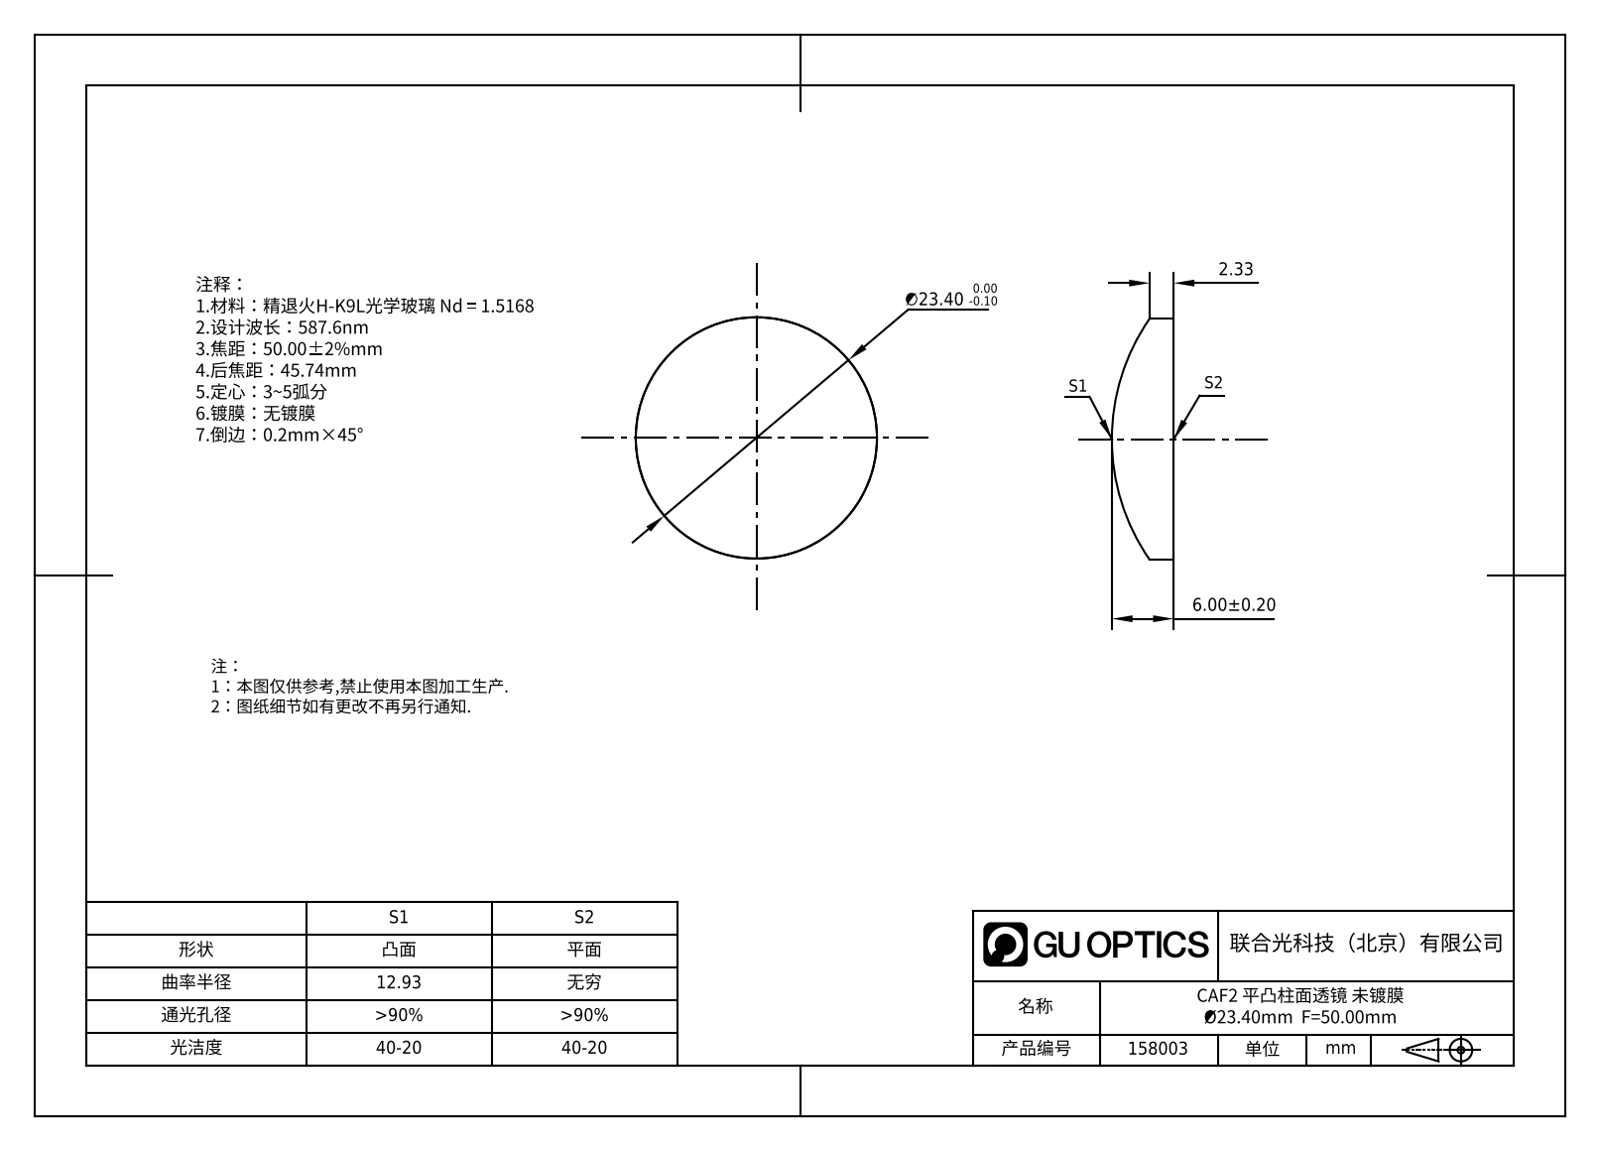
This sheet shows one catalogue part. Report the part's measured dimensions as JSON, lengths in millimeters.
{"part_name": "GL55-025-050", "step_written_by": "SolidWorks 2022 (AUTOMOTIVE_DESIGN)", "units": "millimeters", "bodies": {"solids": 1, "faces": 9, "planar": 1, "cylindrical": 4, "other": 4}, "overall_size": [23.4, 23.4, 6], "volume_mm3": 2199, "surface_area_mm2": 1175, "round_bosses_or_shafts": [[23.4, 1]], "partial_cylinders_radius": [[20.48, 1]]}
